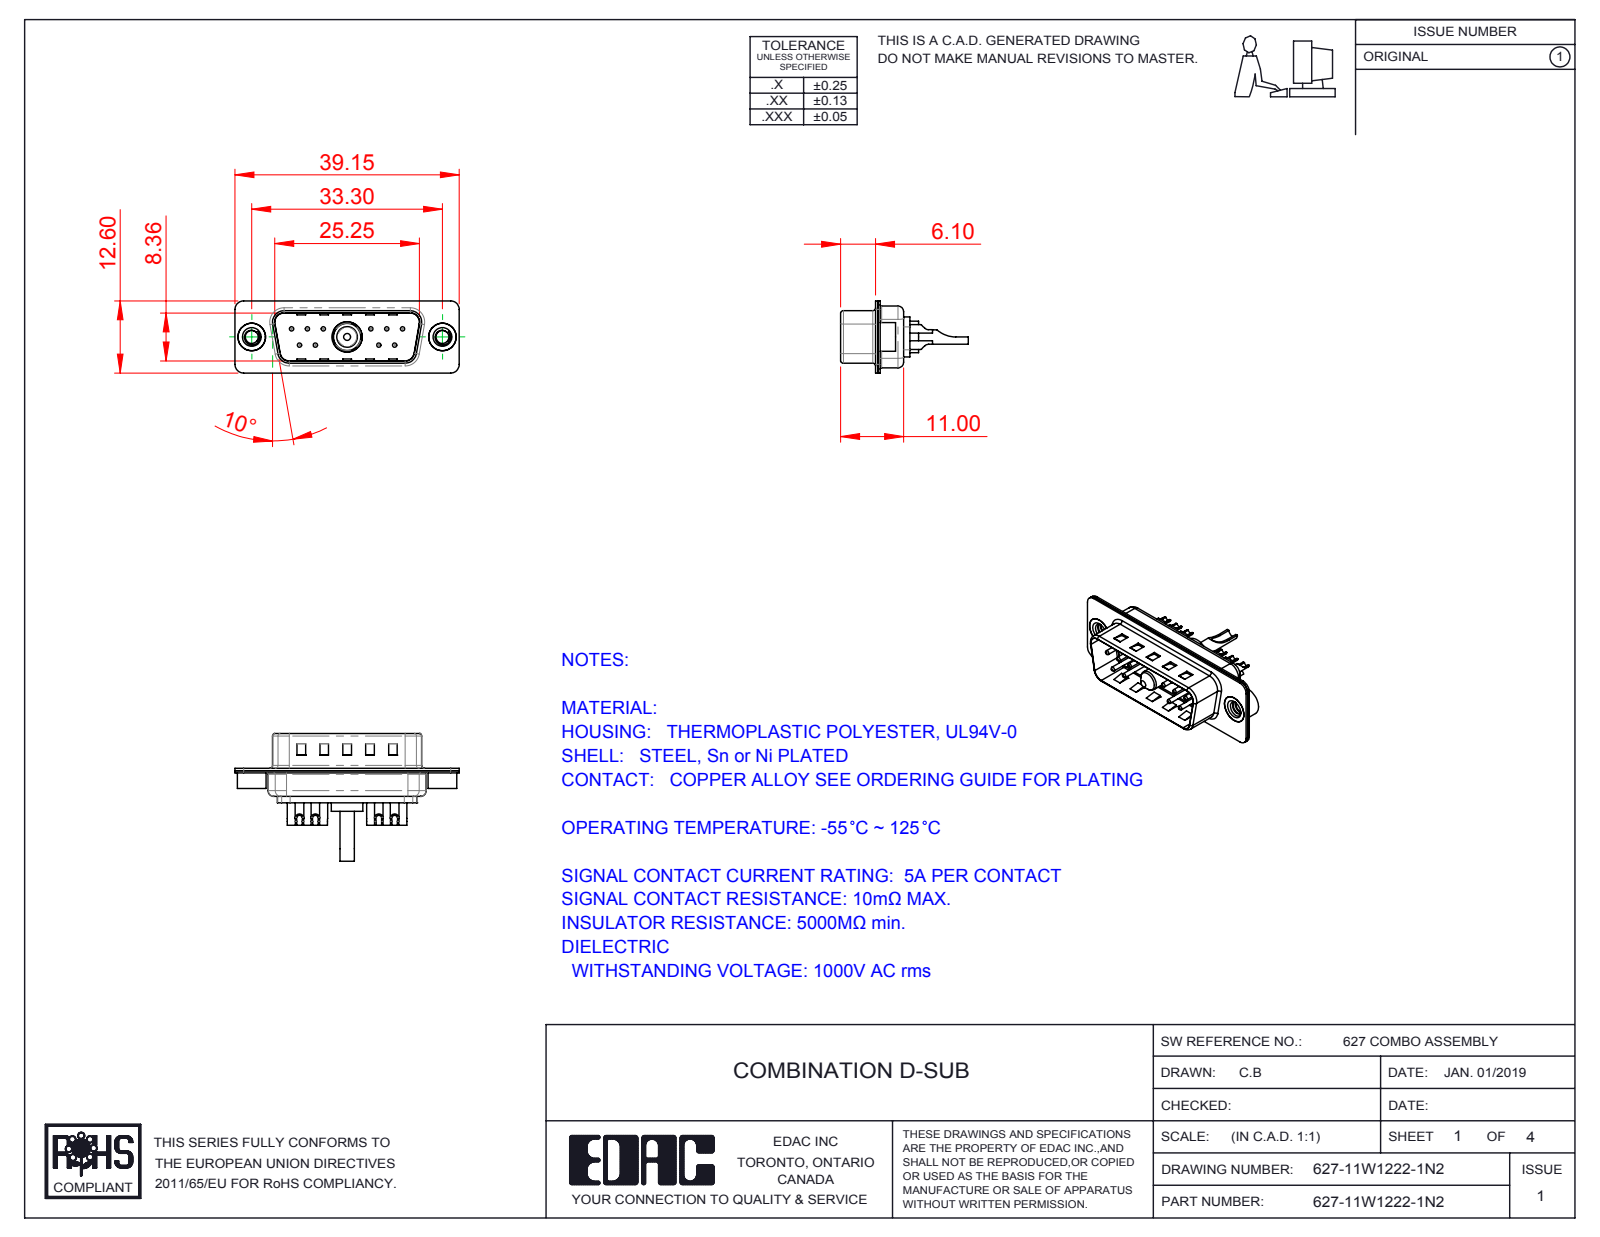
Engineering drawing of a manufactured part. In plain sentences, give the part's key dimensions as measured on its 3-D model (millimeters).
The part is named "627Combo Contact Row 1_22; 627Combo Shell Front_15 Contacts; 627Combo Shell Rear_15 Contacts; Power Pin_10A SC (+4 more)". Its 3-D file was written by "SolidWorks 2016 (CONFIG_CONTROL_DESIGN)". It is 17 solids with 768 faces: 250 planar, 319 cylindrical and 199 other. Overall it measures 39.15 by 22.3 by 12.6 millimeters. Its volume is 1 924 cubic millimeters and its surface area 4 917 square millimeters. Round holes: 10 of diameter 0.75, 10 of diameter 1, 10 of diameter 1.6, 10 of diameter 2, 2 of diameter 2.26, 2 of diameter 4, 2 of diameter 4.8, 1 of diameter 1.7, 1 of diameter 4.85, 1 of diameter 5.3. Round bosses or shafts: 10 of diameter 1.5, 2 of diameter 5, 2 of diameter 4.9, 1 of diameter 5.5, 1 of diameter 5.2, 1 of diameter 4.75, 1 of diameter 3.75, 1 of diameter 3.6. Partial cylindrical surfaces (rounded edges, fillets, slot ends): 20 of radius 1.5, 12 of radius 2, 9 of radius 1, 8 of radius 0.5, 8 of radius 1.6, 4 of radius 0.25, 4 of radius 0.6, 4 of radius 0.65. The main face-to-face distances are 0.4, 0.82, 9.58, 8.76, 0.8, 1.5, 5.6, 1.4, 5.2, 6. The hole center spacings are 3.16, 2.77, 13.85, 11.08, 16.62, 5.03, 5.04, 5.54.
